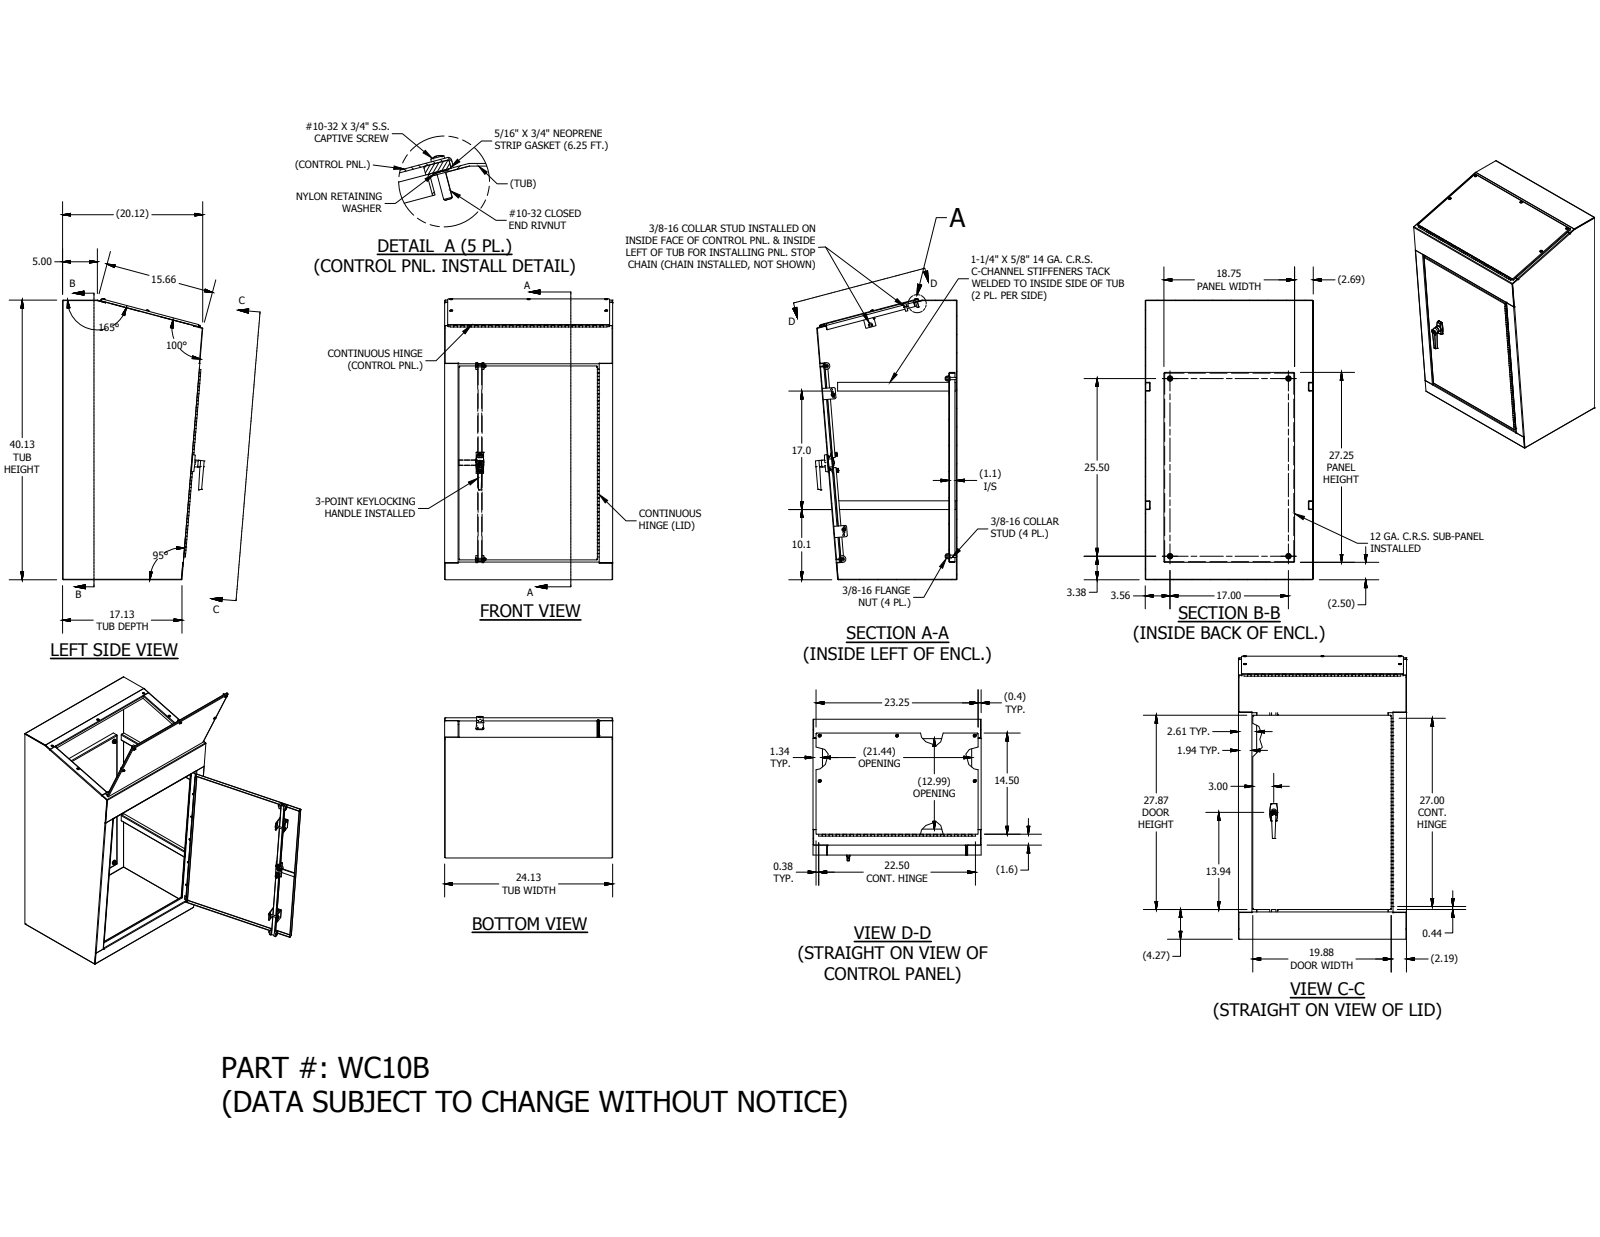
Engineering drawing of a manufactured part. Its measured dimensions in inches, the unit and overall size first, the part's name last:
Units: inches
Overall size (bounding box): 40.357 × 24.125 × 20.32
Round holes (diameter × count): ⌀0.313 ×11, ⌀0.277 ×8, ⌀0.25 ×7, ⌀0.083 ×5, ⌀0.156 ×5, ⌀0.196 ×5, ⌀0.257 ×5, ⌀0.278 ×5, ⌀0.2 ×4, ⌀0.307 ×4, ⌀0.563 ×4, ⌀0.138 ×3
Round bosses / shafts (diameter × count): ⌀0.157 ×7, ⌀0.33 ×6, ⌀0.453 ×5, ⌀0.406 ×5, ⌀0.248 ×5, ⌀0.167 ×5, ⌀0.625 ×4, ⌀0.533 ×4
Partial cylindrical surfaces — rounded edges, fillets, slot ends (radius × count): R0.031 ×42, R0.105 ×36, R0.008 ×27, R0.025 ×16, R0.03 ×8, R0.05 ×8, R0.051 ×8, R0.121 ×8
Main face-to-face distances: 0.074, 24.051, 23.977, 24.125, 0.094, 1.168, 1.094, 1.074, 1, 40.051
Hole centre spacings: 1.154, 22.25, 11.125, 0.875, 11.125, 6.5, 0.906, 0.907
Volume: 428.7 in³ · Surface area: 11 097 in²
Bodies: 71 solids, 2646 faces (1486 planar, 742 cylindrical, 418 other)
Part name (STEP PRODUCT): WC10B
STEP written by: SolidWorks 2019 (AUTOMOTIVE_DESIGN)
